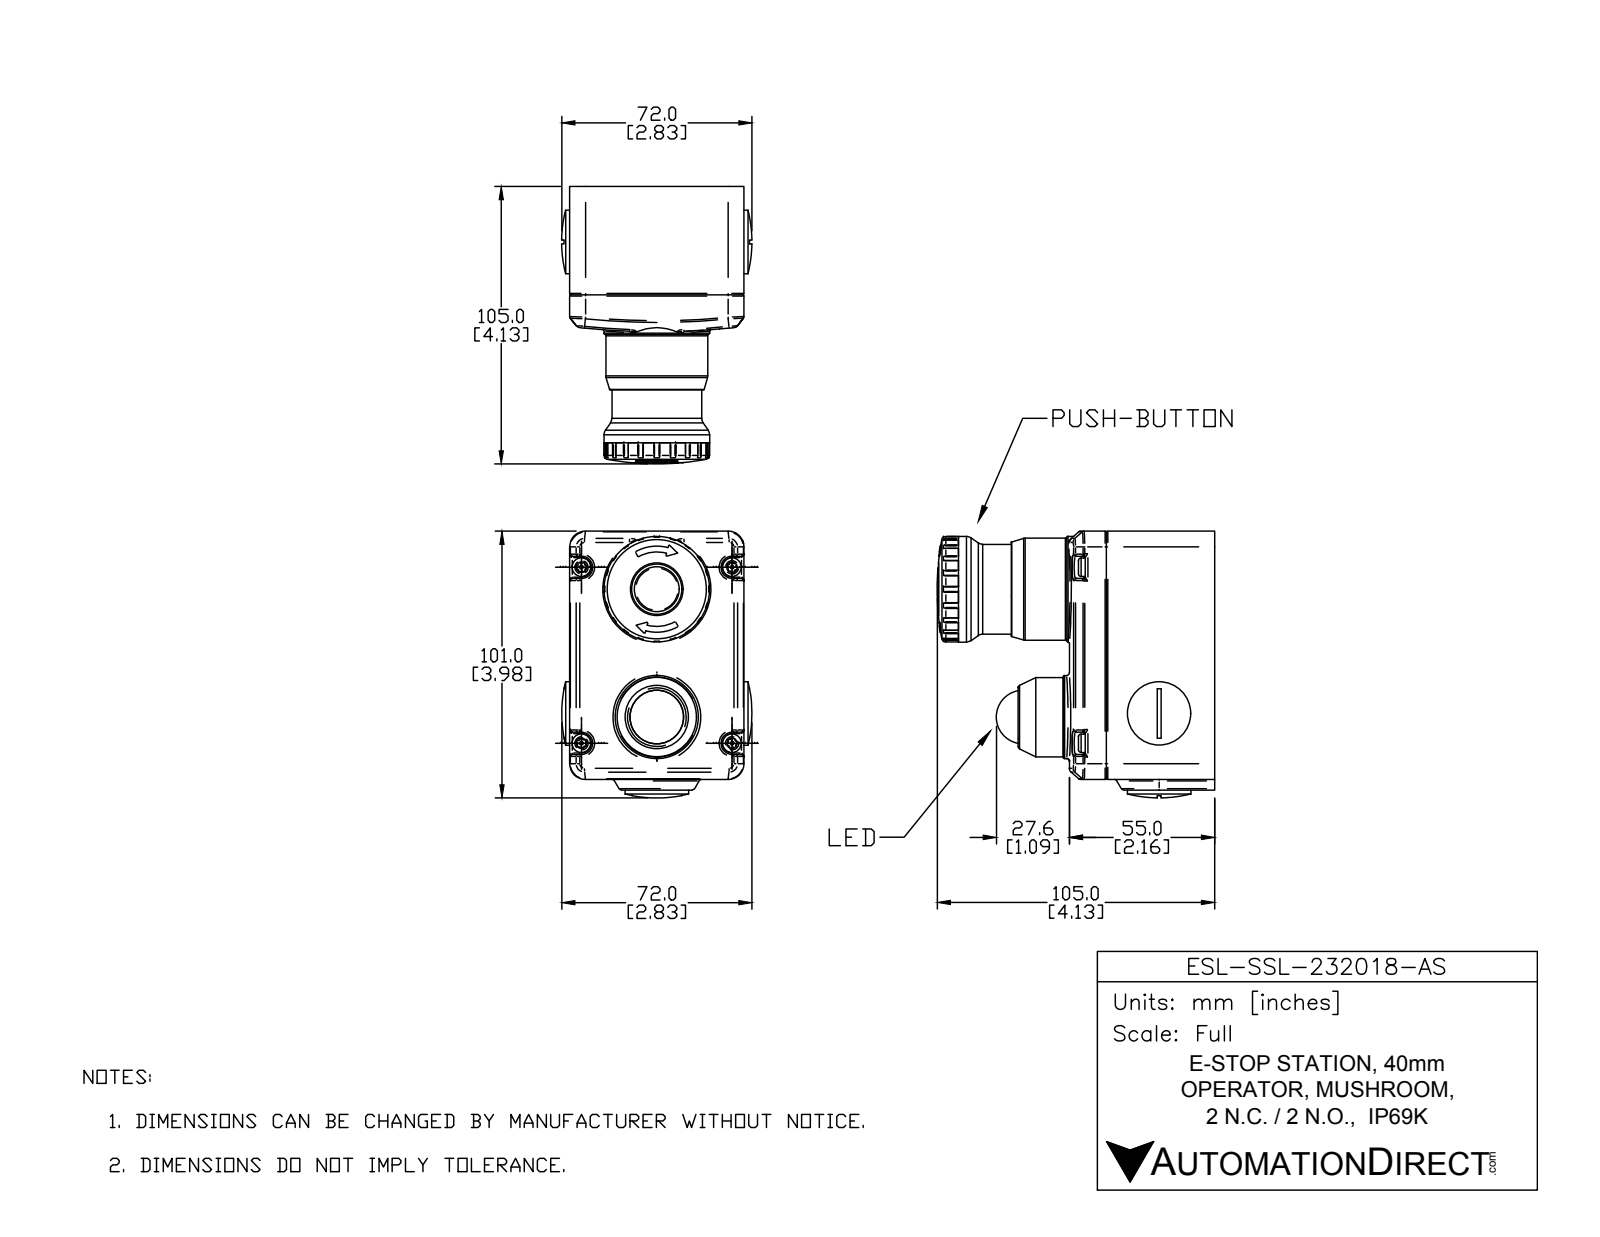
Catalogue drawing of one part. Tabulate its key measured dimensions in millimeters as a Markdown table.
| quantity | value |
| --- | --- |
| part name | ESL-SSL-232018-AS |
| STEP written by | SolidWorks 2016 (AUTOMOTIVE_DESIGN) |
| units | millimeters |
| bodies | 13 solids, 695 faces (221 planar, 256 cylindrical, 218 other) |
| overall size | 105 × 100.99 × 71.98 |
| volume | 369 953 mm³ |
| surface area | 65 813 mm² |
| round holes (diameter × count) | 4.5 × 4, 28.04 × 1, 31.1 × 1, 37 × 1 |
| round bosses / shafts (diameter × count) | 7 × 4, 1 × 4, 24 × 2, 40 × 1, 38.6 × 1, 34 × 1, 31.4 × 1, 30 × 1 |
| partial cylindrical surfaces (radius × count) | 0.1 × 80, 0.76 × 24, 0.5 × 14, 0.2 × 4, 1 × 4, 4.2 × 4, 6 × 4, 2 × 2 |
| main face-to-face distances | 41, 66, 56, 15, 98, 4, 94, 56.8, 15.8, 0.8 |
| hole center spacings | 31.38, 32.23, 54, 69.83, 71.31, 82, 98.18, 48.4 |
